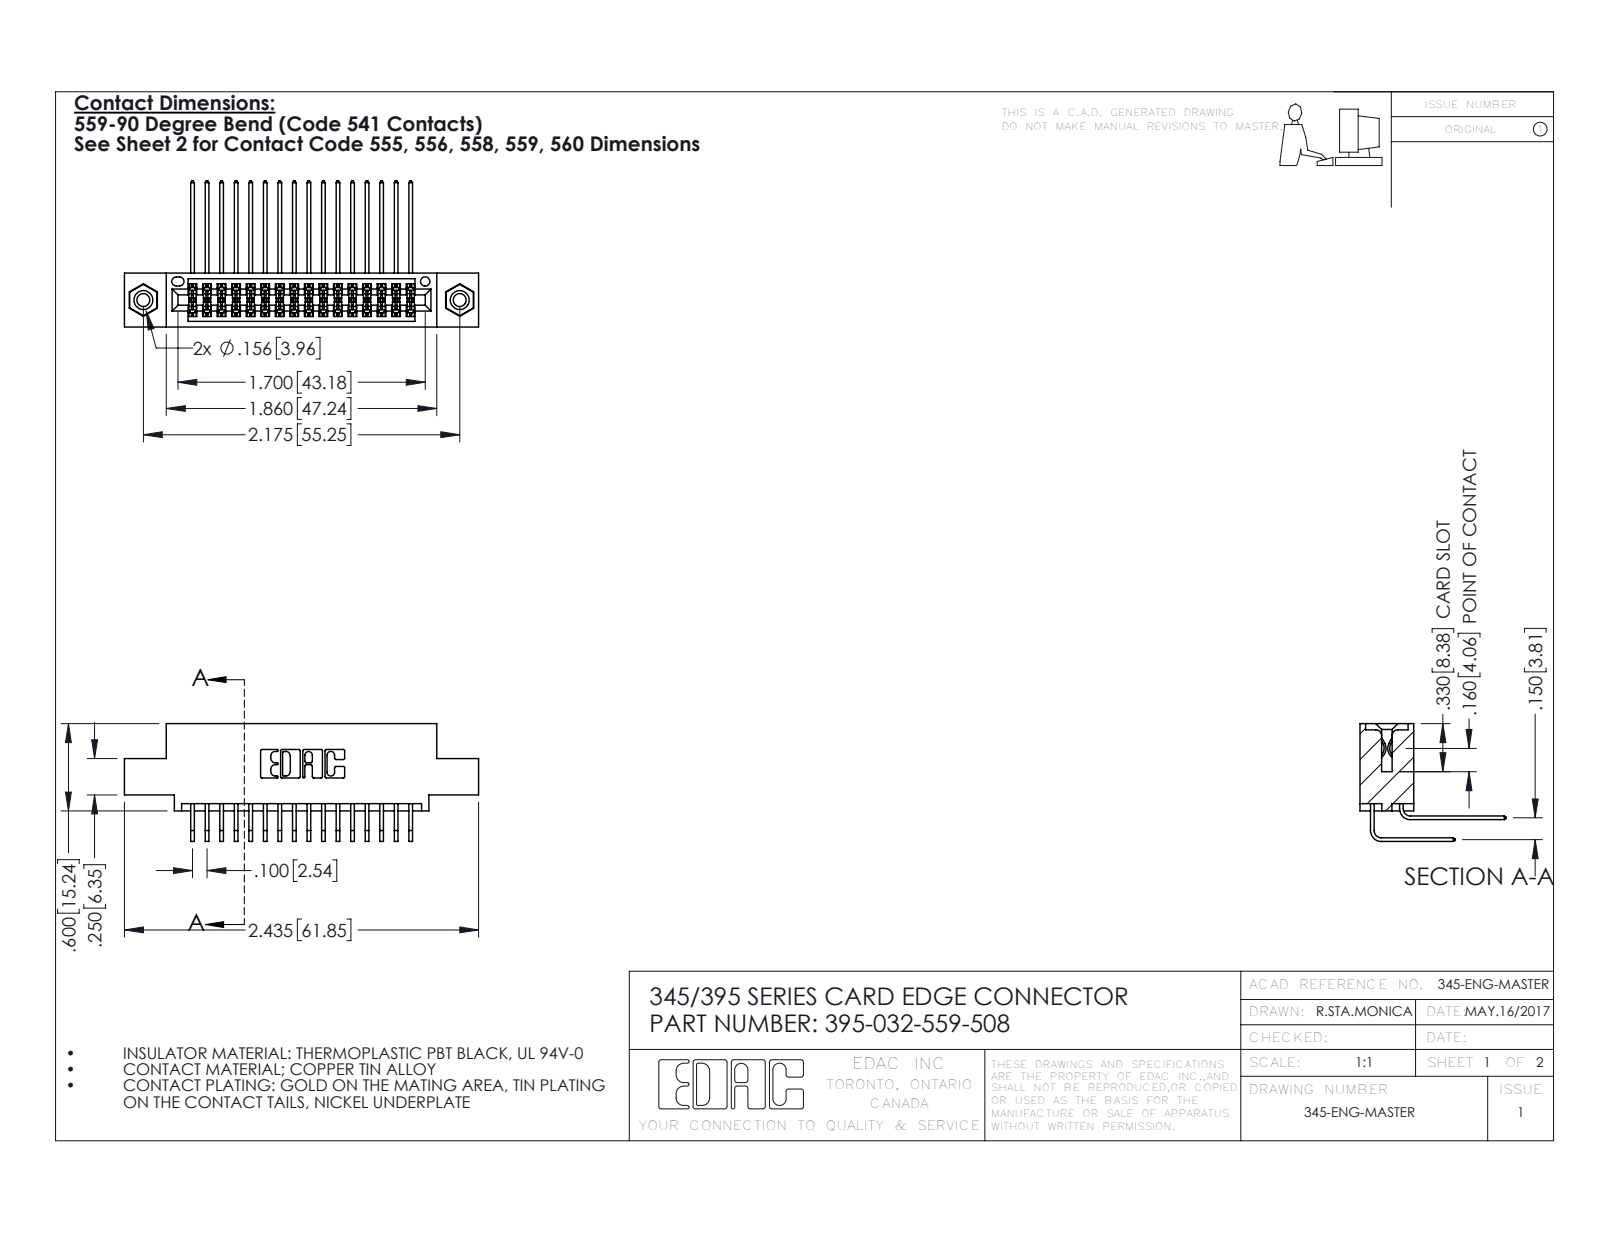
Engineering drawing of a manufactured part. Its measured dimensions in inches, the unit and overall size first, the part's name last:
Units: inches
Overall size (bounding box): 2.435 × 1.005 × 0.809
Round holes (diameter × count): ⌀0.089 ×2, ⌀0.125 ×2, ⌀0.156 ×2, ⌀0.064 ×1
Round bosses / shafts (diameter × count): ⌀0.155 ×2
Partial cylindrical surfaces — rounded edges, fillets, slot ends (radius × count): R0.006 ×49, R0.01 ×22, R0.007 ×6, R0.031 ×6, R0.026 ×3, R0.014 ×2, R0.019 ×2, R0.022 ×2
Main face-to-face distances: 0.072, 0.298, 0.2, 0.37, 0.098, 0.272, 0.025, 0.225, 0.15, 0.175
Hole centre spacings: 0.27, 1.942, 2.175
Volume: 0.358 in³ · Surface area: 14.18 in²
Bodies: 35 solids, 1854 faces (1236 planar, 602 cylindrical, 16 other)
Part name (STEP PRODUCT): 345-292-001_558 559 Tail - 1; 395-032-559-508; 345-250-001_345-250-003-102; 345-292-001_559 Tail - 2 (+1 more)
STEP written by: SolidWorks 2016 (CONFIG_CONTROL_DESIGN)
